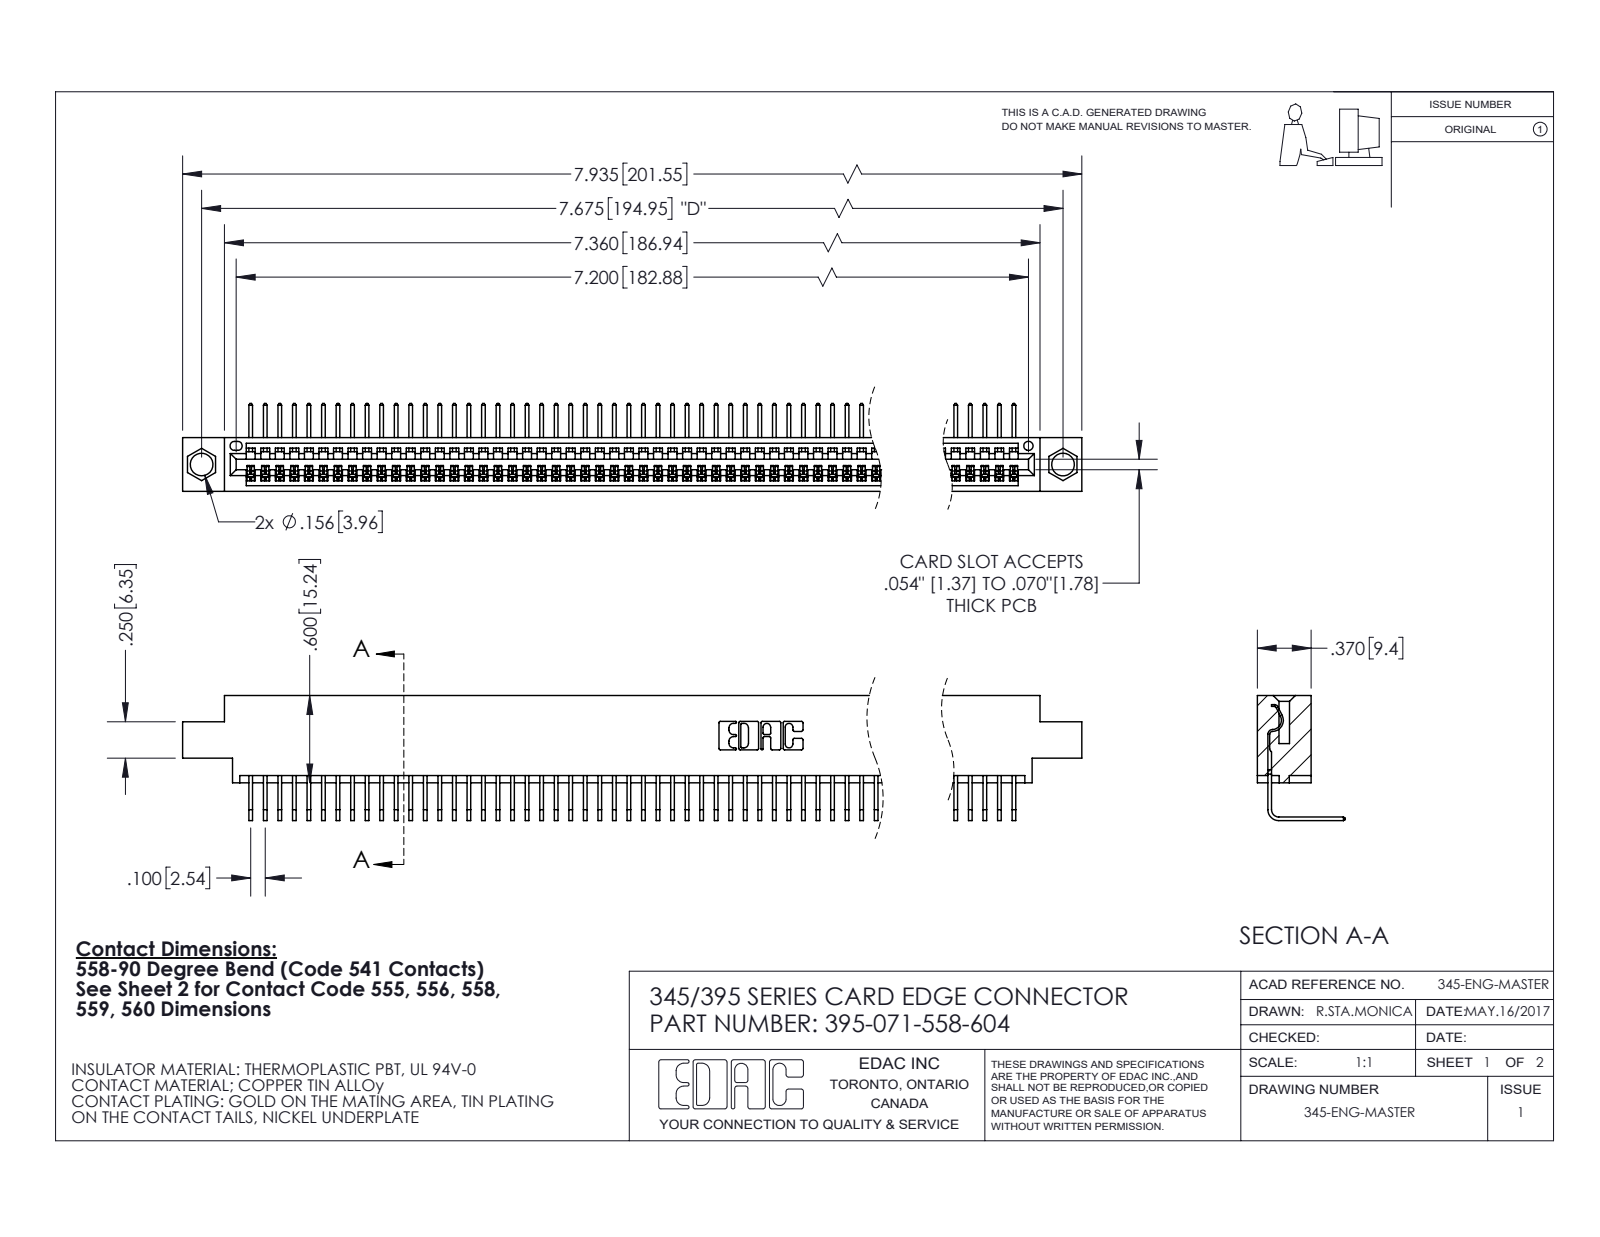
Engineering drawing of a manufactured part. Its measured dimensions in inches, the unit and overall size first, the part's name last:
Units: inches
Overall size (bounding box): 7.935 × 0.859 × 0.605
Round holes (diameter × count): ⌀0.156 ×2, ⌀0.064 ×1
Partial cylindrical surfaces — rounded edges, fillets, slot ends (radius × count): R0.006 ×142, R0.01 ×22, R0.007 ×6, R0.031 ×6, R0.026 ×3, R0.031 ×2, R0.04 ×2, R0.014 ×1
Main face-to-face distances: 0.072, 0.298, 0.37, 0.2, 0.098, 0.272, 0.025, 0.225, 0.175, 0.149
Hole centre spacings: 0.27, 7.439, 7.675
Volume: 1.184 in³ · Surface area: 42.67 in²
Bodies: 72 solids, 4404 faces (3080 planar, 1324 cylindrical, 0 other)
Part name (STEP PRODUCT): 395-071-558-604; 345 Part_0.170 Offset - 0.156 Dia-TI; 345-292-001_558 Tail - 2
STEP written by: SolidWorks 2020 (CONFIG_CONTROL_DESIGN)
